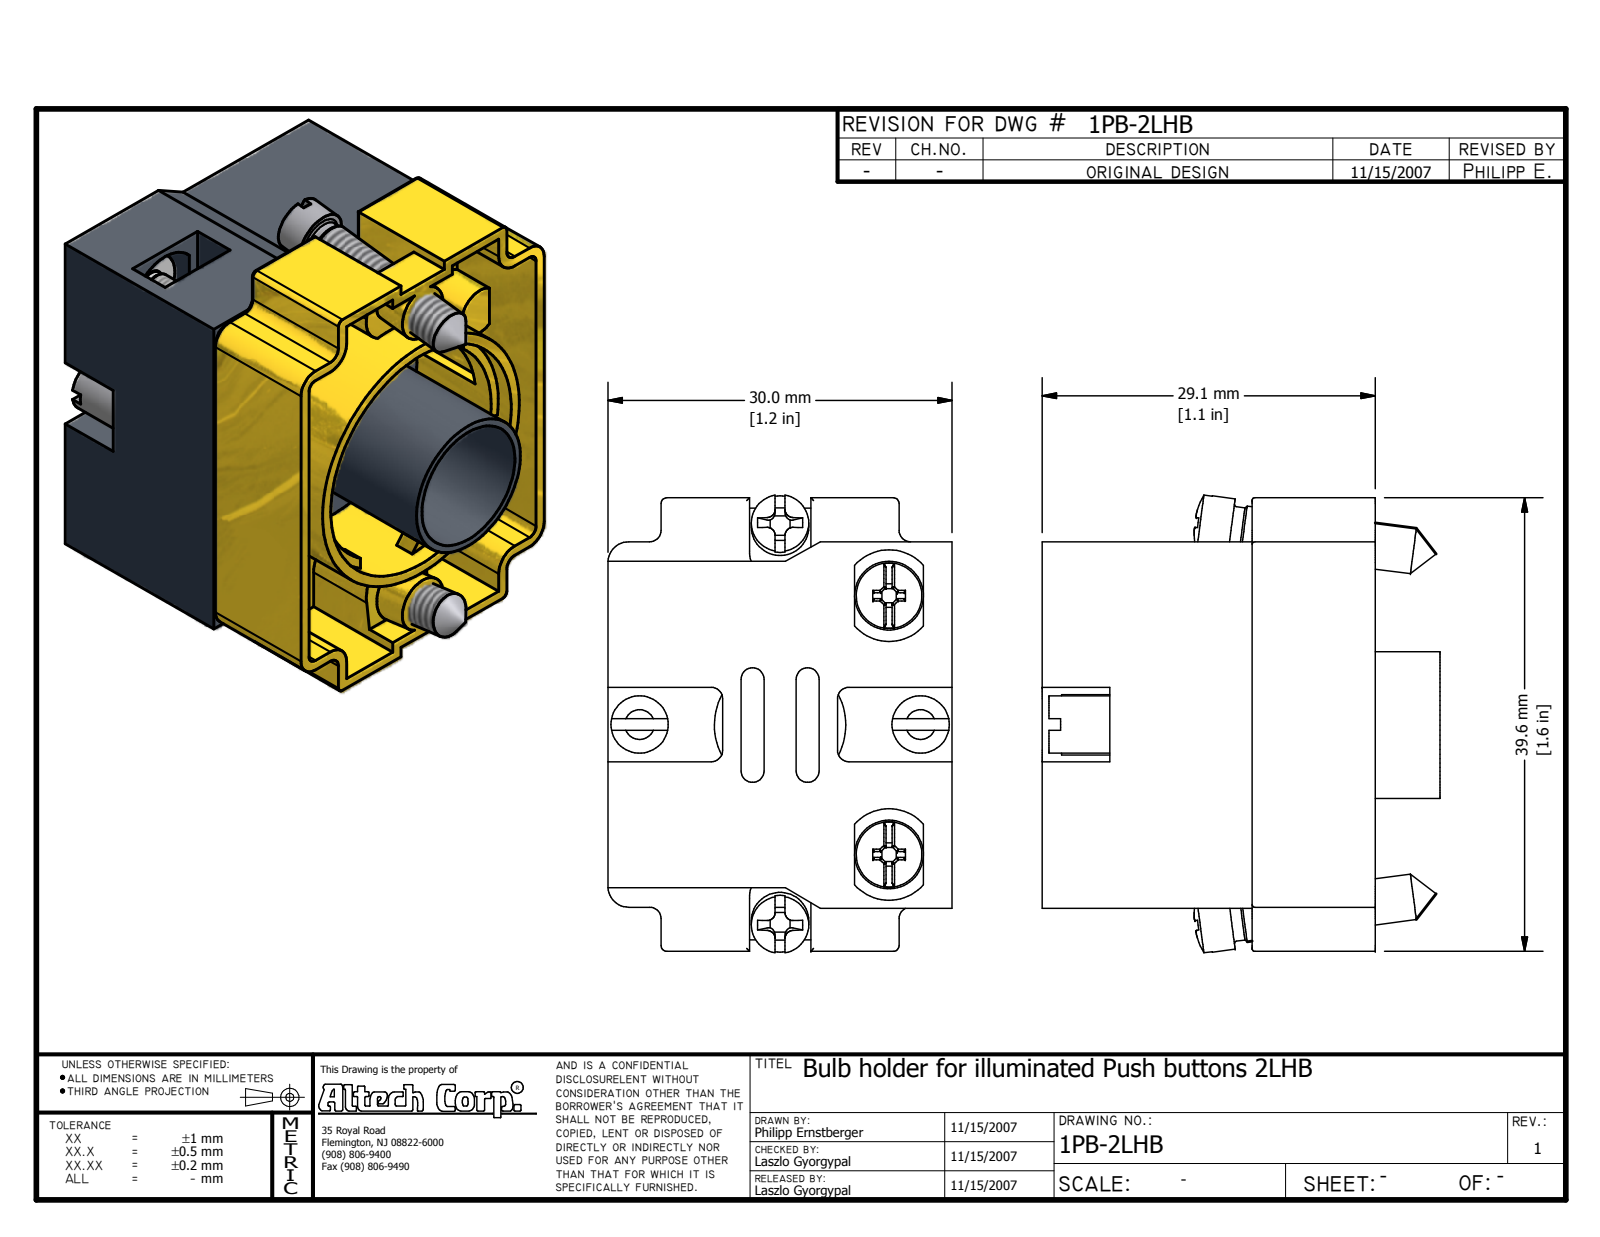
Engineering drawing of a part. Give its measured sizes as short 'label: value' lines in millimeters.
name: 2LHB+2BRK; 2BRK; DIN 7985 (Z) M4x18-Z; 2LHB (+3 more)
written by: Autodesk Inventor 2008 (AUTOMOTIVE_DESIGN)
unit: mm
bodies: 9 solids, 408 faces (205 planar, 94 cylindrical, 109 other)
size: 42.12 × 39.97 × 30
volume: 19 090 mm³; area: 15 555 mm²
holes: 5× ⌀2.5, 2× ⌀2.6, 1× ⌀3, 1× ⌀22.25
bosses: 4× ⌀5, 3× ⌀3, 2× ⌀4, 2× ⌀3.65, 2× ⌀2.75, 1× ⌀24.25, 1× ⌀12.8, 1× ⌀10.2
rounds: 10× R0.25, 8× R0.72, 8× R1, 5× R2.25, 4× R0.5, 4× R0.8, 4× R1.8, 4× R2
face distances: 1, 30, 18.3, 29, 19.3, 28.5, 5.55, 34.05, 3.85, 1.7
hole spacings: 14.53, 6.52, 6.57, 13, 25.88, 26, 26.27, 29.07
